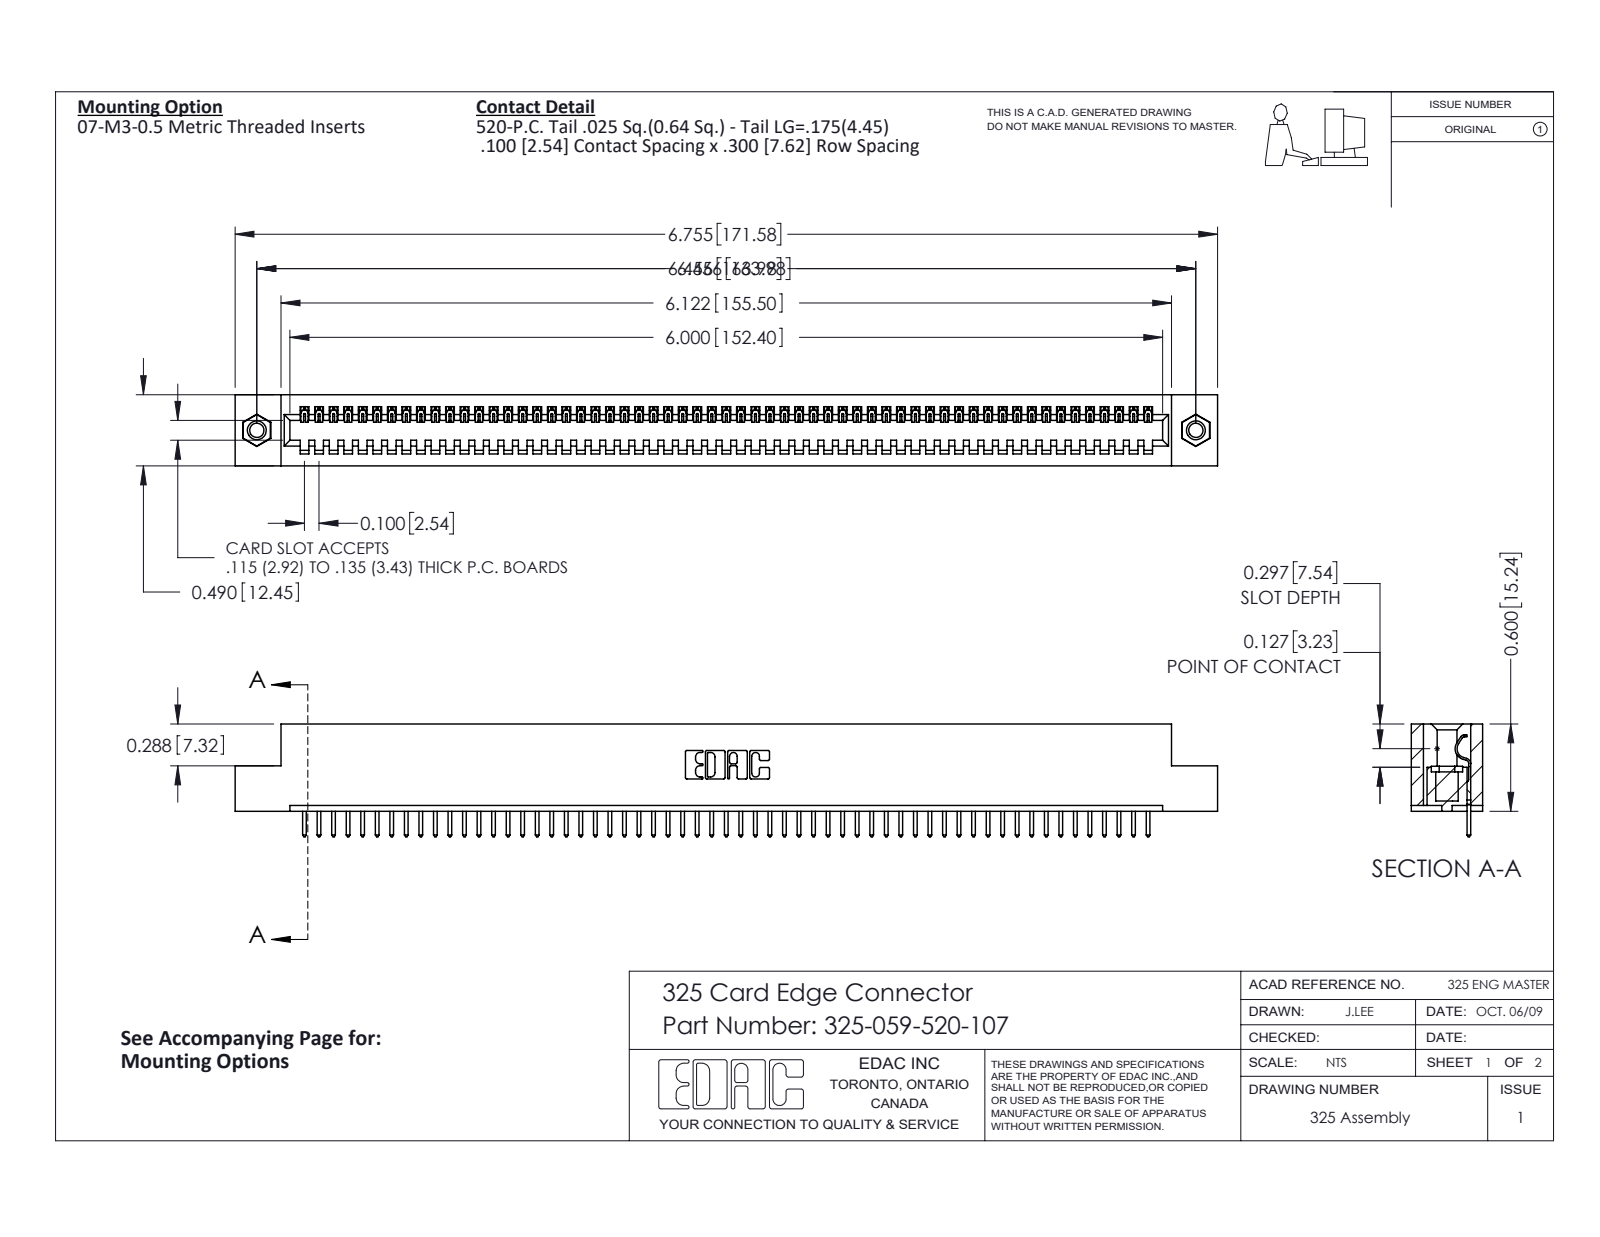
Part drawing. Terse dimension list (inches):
name: 325 Part_TI; 345-250-001_345-250-005-103; 325-059-520-107; 325-292-001_325-293-120
written by: SolidWorks 2016 (CONFIG_CONTROL_DESIGN)
unit: in
bodies: 62 solids, 3596 faces (2580 planar, 1000 cylindrical, 16 other)
size: 6.755 × 0.775 × 0.49
volume: 1.327 in³; area: 36.36 in²
holes: 2× ⌀0.098, 2× ⌀0.125, 2× ⌀0.16
bosses: 2× ⌀0.155
rounds: 118× R0.006, 118× R0.01, 22× R0.01, 6× R0.007, 6× R0.031, 3× R0.026, 1× R0.014, 1× R0.022
face distances: 0.083, 0.407, 0.49, 0.3, 0.107, 0.383, 0.025, 0.325, 0.56, 0.263
hole spacings: 6.456
